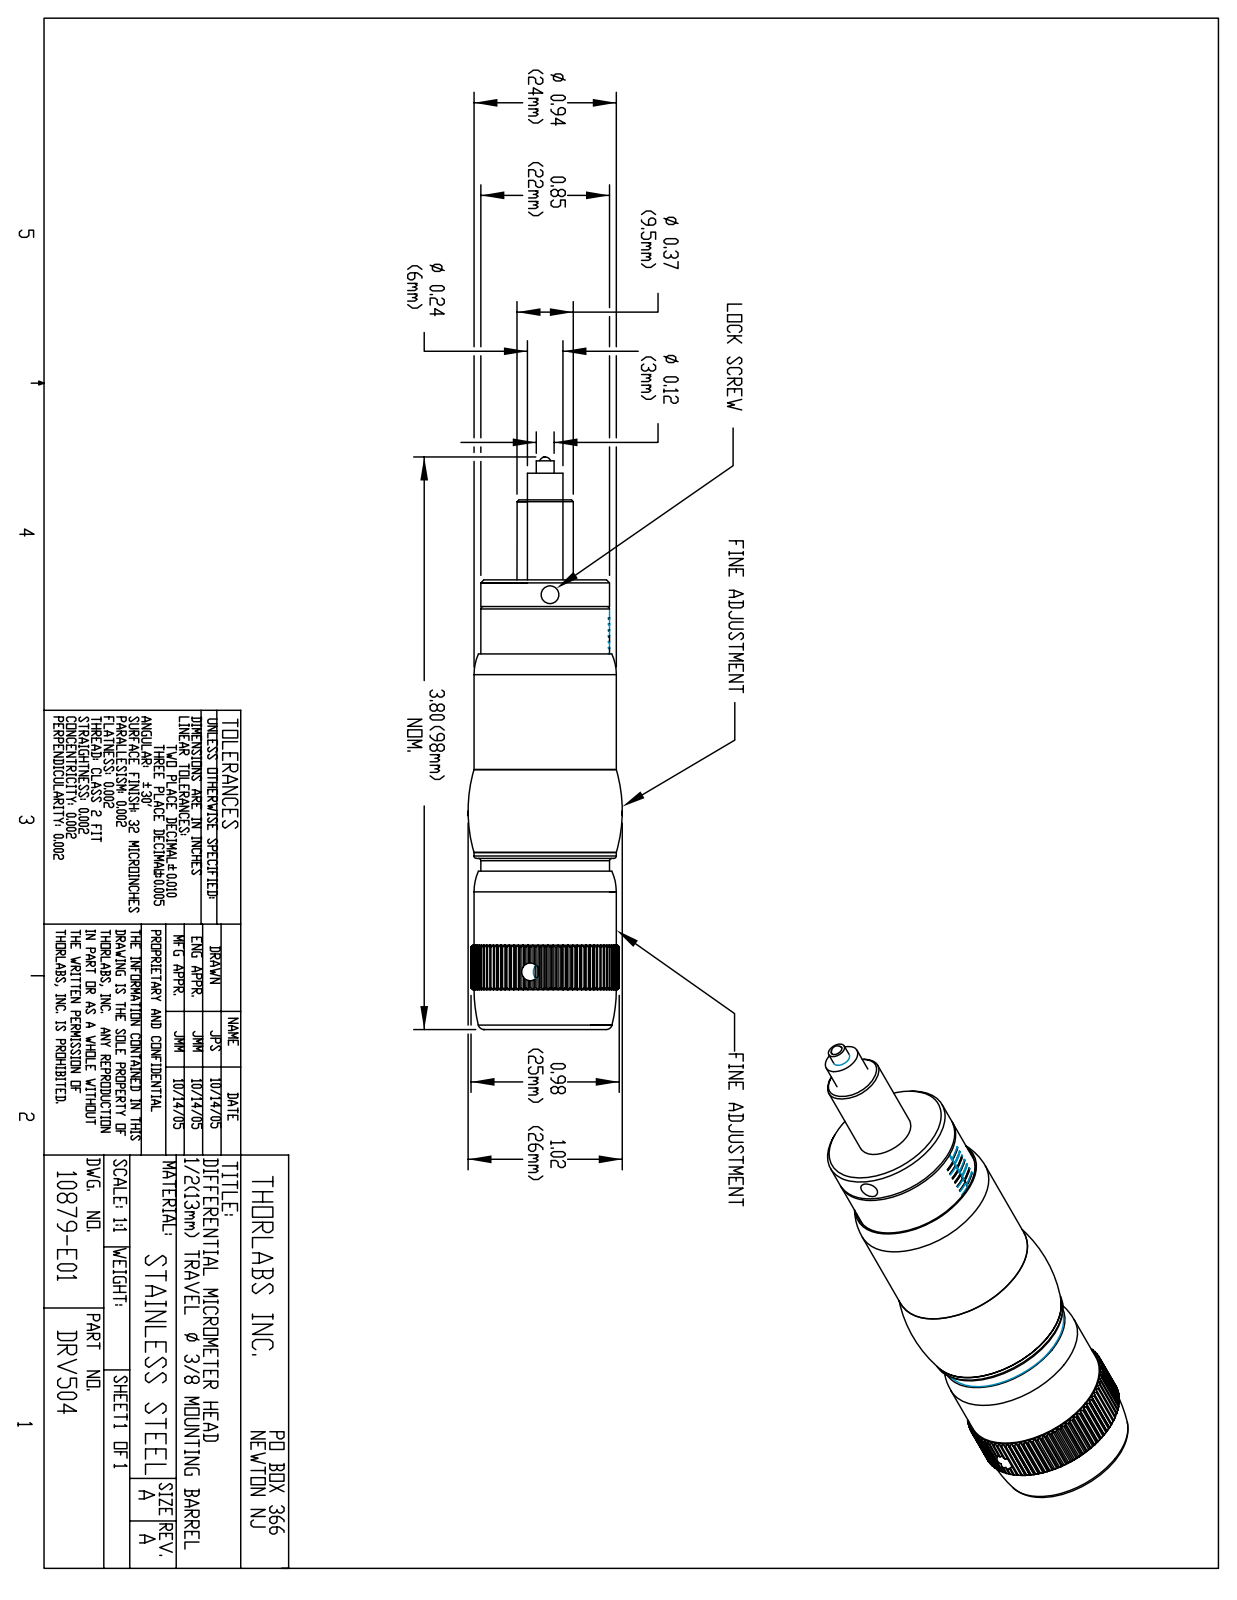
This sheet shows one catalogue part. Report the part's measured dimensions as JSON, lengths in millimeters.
{"part_name": "10879-E0W", "step_written_by": "SolidWorks 2007 (AUTOMOTIVE_DESIGN)", "units": "millimeters", "bodies": {"solids": 0, "faces": 548, "planar": 216, "cylindrical": 120, "other": 212}, "overall_size": [96.6, 26, 26], "round_holes": [[3, 2], [2, 1], [22, 1]], "round_bosses_or_shafts": [[24, 1], [21.7, 1], [9.5, 1], [6, 1], [3, 1]], "partial_cylinders_radius": [[10.8, 1], [12.5, 1]], "face_to_face_distances": [4.5, 17.2, 17.2, 18, 17.3, 13.5, 49.1, 12.5, 42.5, 47]}
